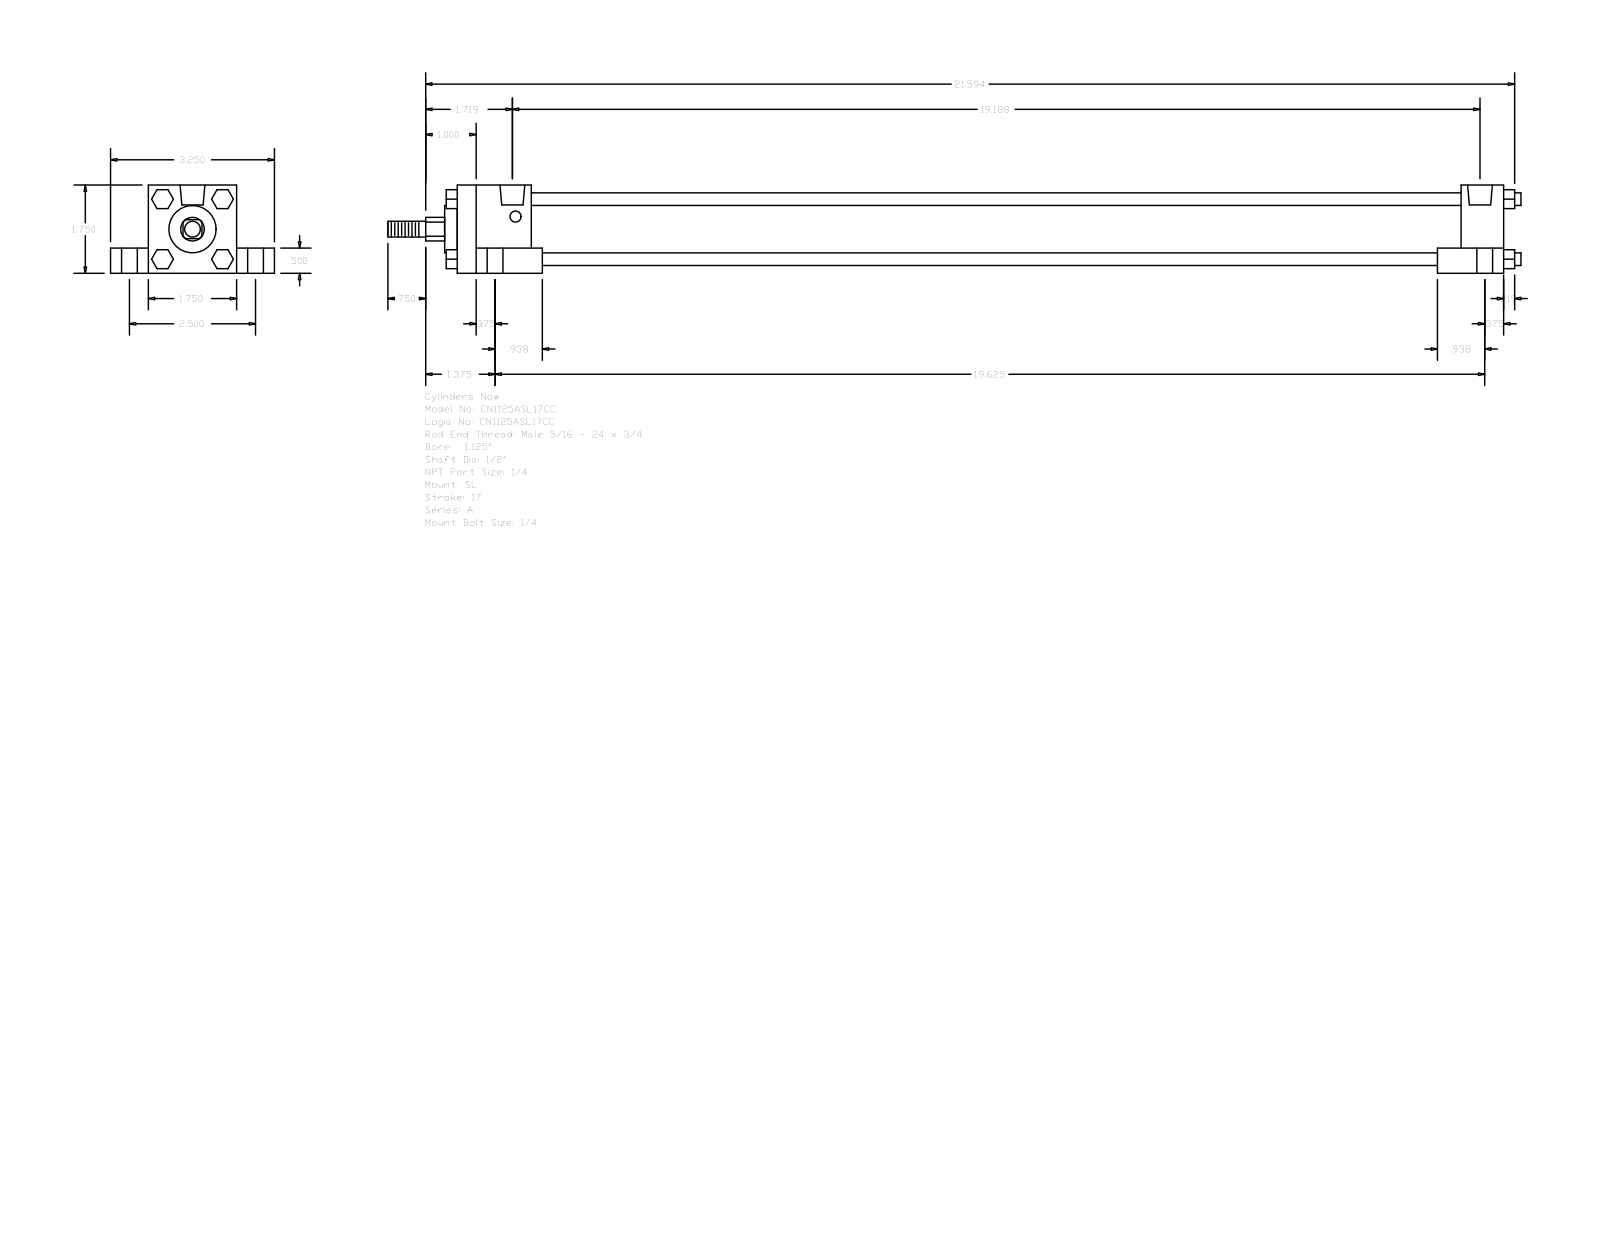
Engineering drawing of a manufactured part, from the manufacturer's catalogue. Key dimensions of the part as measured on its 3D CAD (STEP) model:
Part name (STEP PRODUCT): A_SL__0112_0.5
STEP written by: GSSL Pune (CONFIG_CONTROL_DESIGN)
Units: millimetres
Bodies: 0 solids, 150 faces (114 planar, 36 cylindrical, 0 other)
Overall size (bounding box): 570.71 × 82.55 × 44.45
Round holes (diameter × count): ⌀5.56 ×4, ⌀7.94 ×4, ⌀14.29 ×4, ⌀12.49 ×2
Round bosses / shafts (diameter × count): ⌀6.35 ×4, ⌀31.88 ×1, ⌀23.81 ×1, ⌀12.7 ×1, ⌀7.94 ×1
Partial cylindrical surfaces — rounded edges, fillets, slot ends (radius × count): R5.94 ×1
Main face-to-face distances: 44.46, 31.76, 12.7, 19.04, 63.5, 489.74, 527.04, 505.61, 21.43, 37.3
Hole centre spacings: 31.84, 32, 32.93, 33.39, 63.5, 484.19, 489.19, 490.77
